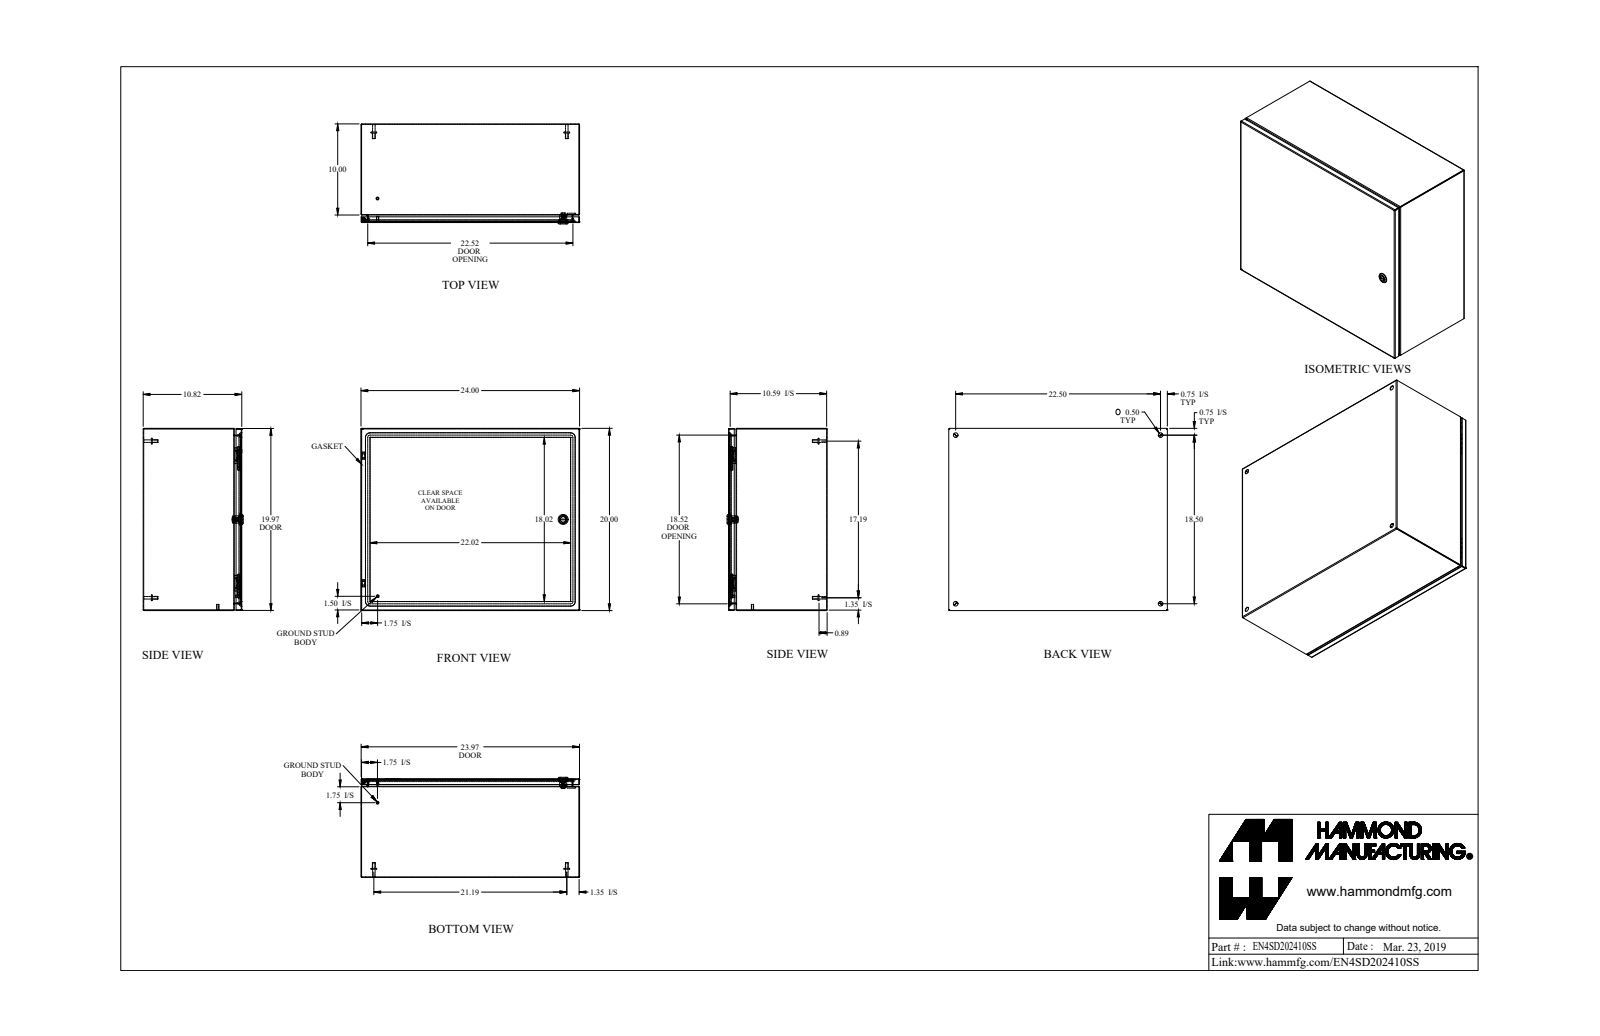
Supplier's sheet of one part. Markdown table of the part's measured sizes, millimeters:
| quantity | value |
| --- | --- |
| part name | EN4SD202410SS_Default |
| STEP written by | SolidWorks 2019 (CONFIG_CONTROL_DESIGN) |
| units | millimeters |
| bodies | 22 solids, 657 faces (303 planar, 212 cylindrical, 142 other) |
| overall size | 609.6 × 508 × 278.9 |
| volume | 2 019 000 mm³ |
| surface area | 2 722 000 mm² |
| round holes (diameter × count) | 12.7 × 5, 4.4 × 1, 5 × 1, 6.1 × 1, 6.1 × 1, 9.8 × 1, 16 × 1, 19.5 × 1 |
| round bosses / shafts (diameter × count) | 8 × 6, 15.9 × 5, 7 × 4, 6.4 × 2, 27.9 × 1, 19.9 × 1, 13.3 × 1, 11.6 × 1 |
| partial cylindrical surfaces (radius × count) | 0.7 × 21, 2.2 × 21, 4.8 × 12, 0.2 × 4, 1.6 × 4, 6.4 × 4, 12.7 × 4, 3.2 × 2 |
| main face-to-face distances | 1.4, 273.4, 272, 274.9, 506.6, 608.2, 505.1, 508, 606.7, 609.6 |
| hole center spacings | 469.9, 571.5, 593.1, 739.9, 236.5, 236.5 |
